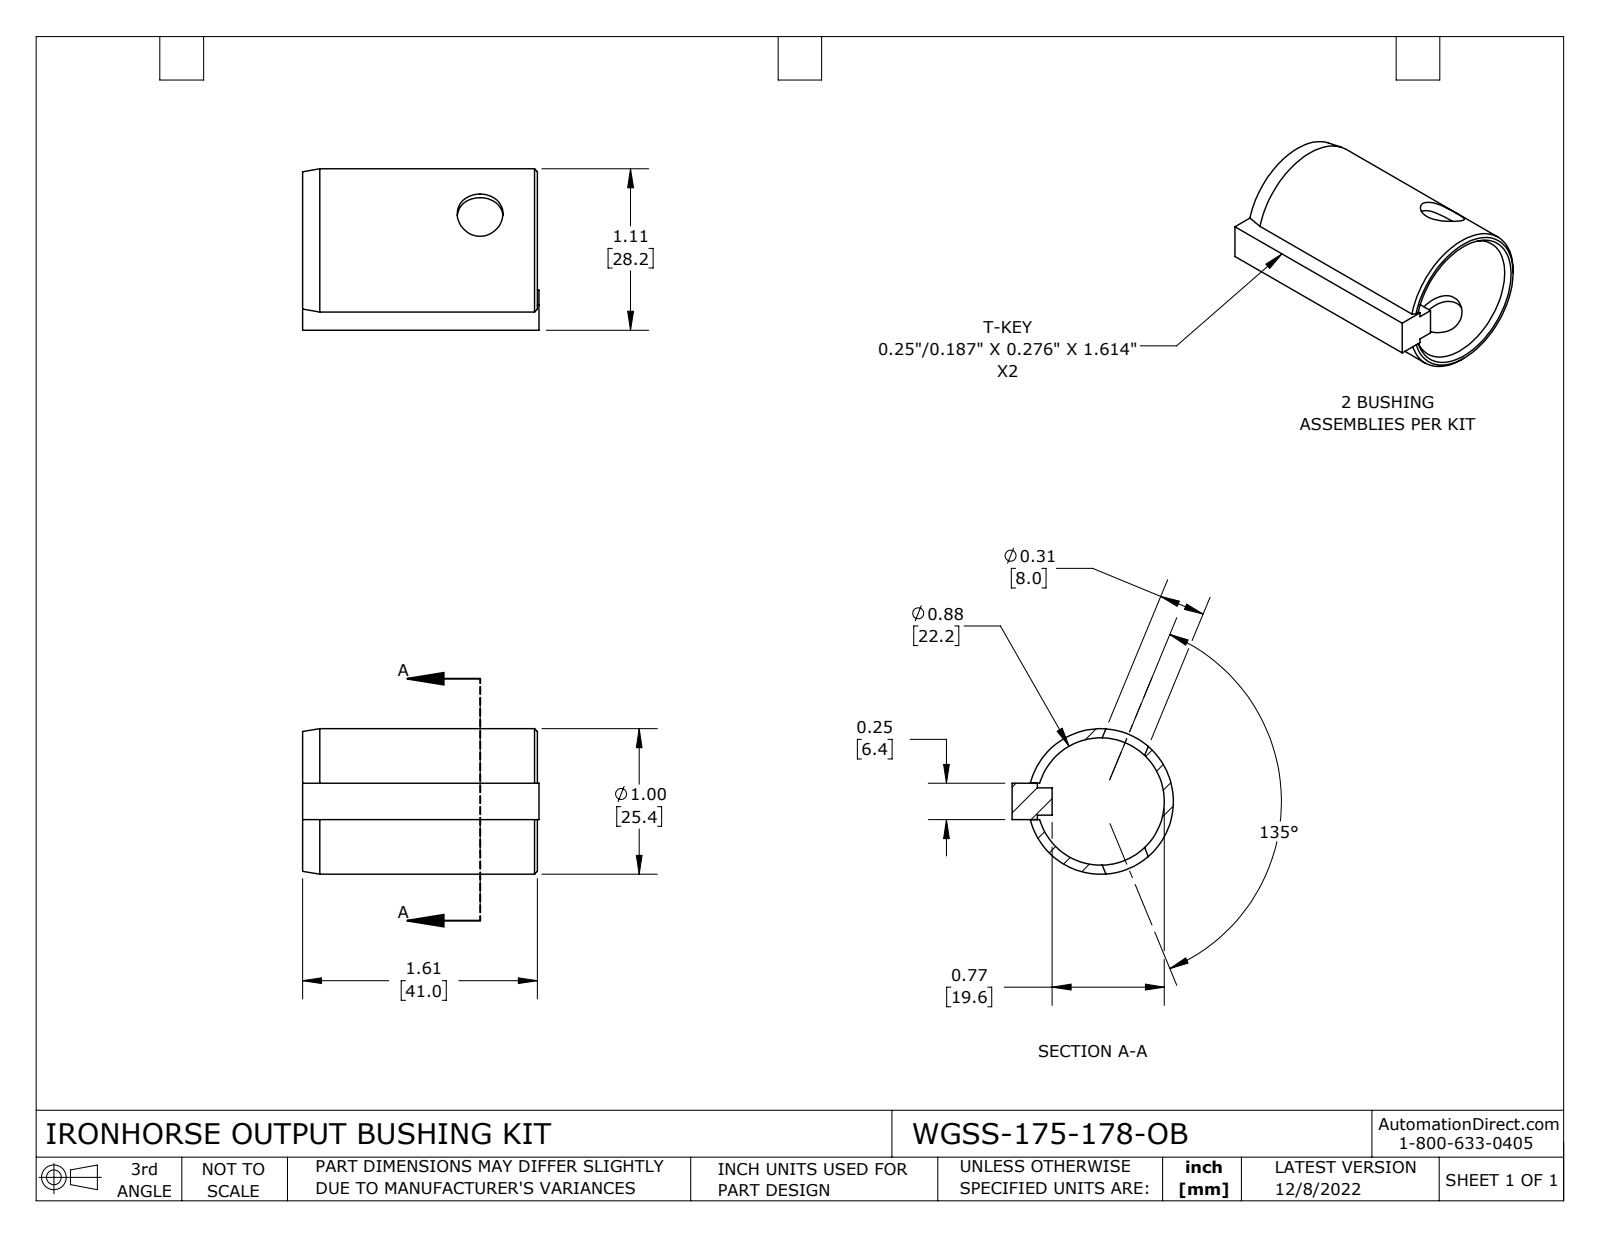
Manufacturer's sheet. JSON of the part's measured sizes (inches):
{"part_name": "WGSS-175-178-OB", "step_written_by": "SolidWorks 2021 (CONFIG_CONTROL_DESIGN)", "units": "inches", "bodies": {"solids": 2, "faces": 35, "planar": 14, "cylindrical": 10, "other": 11}, "overall_size": [1.625, 1.109, 1], "volume_in3": 0.357, "surface_area_in2": 10.7, "round_holes": [[0.315, 2], [0.875, 1]], "round_bosses_or_shafts": [[1, 1]], "face_to_face_distances": [0.25, 0.276, 0.031, 0.219, 0.187, 0.219, 0.031, 0.102, 0.174, 1.625]}
